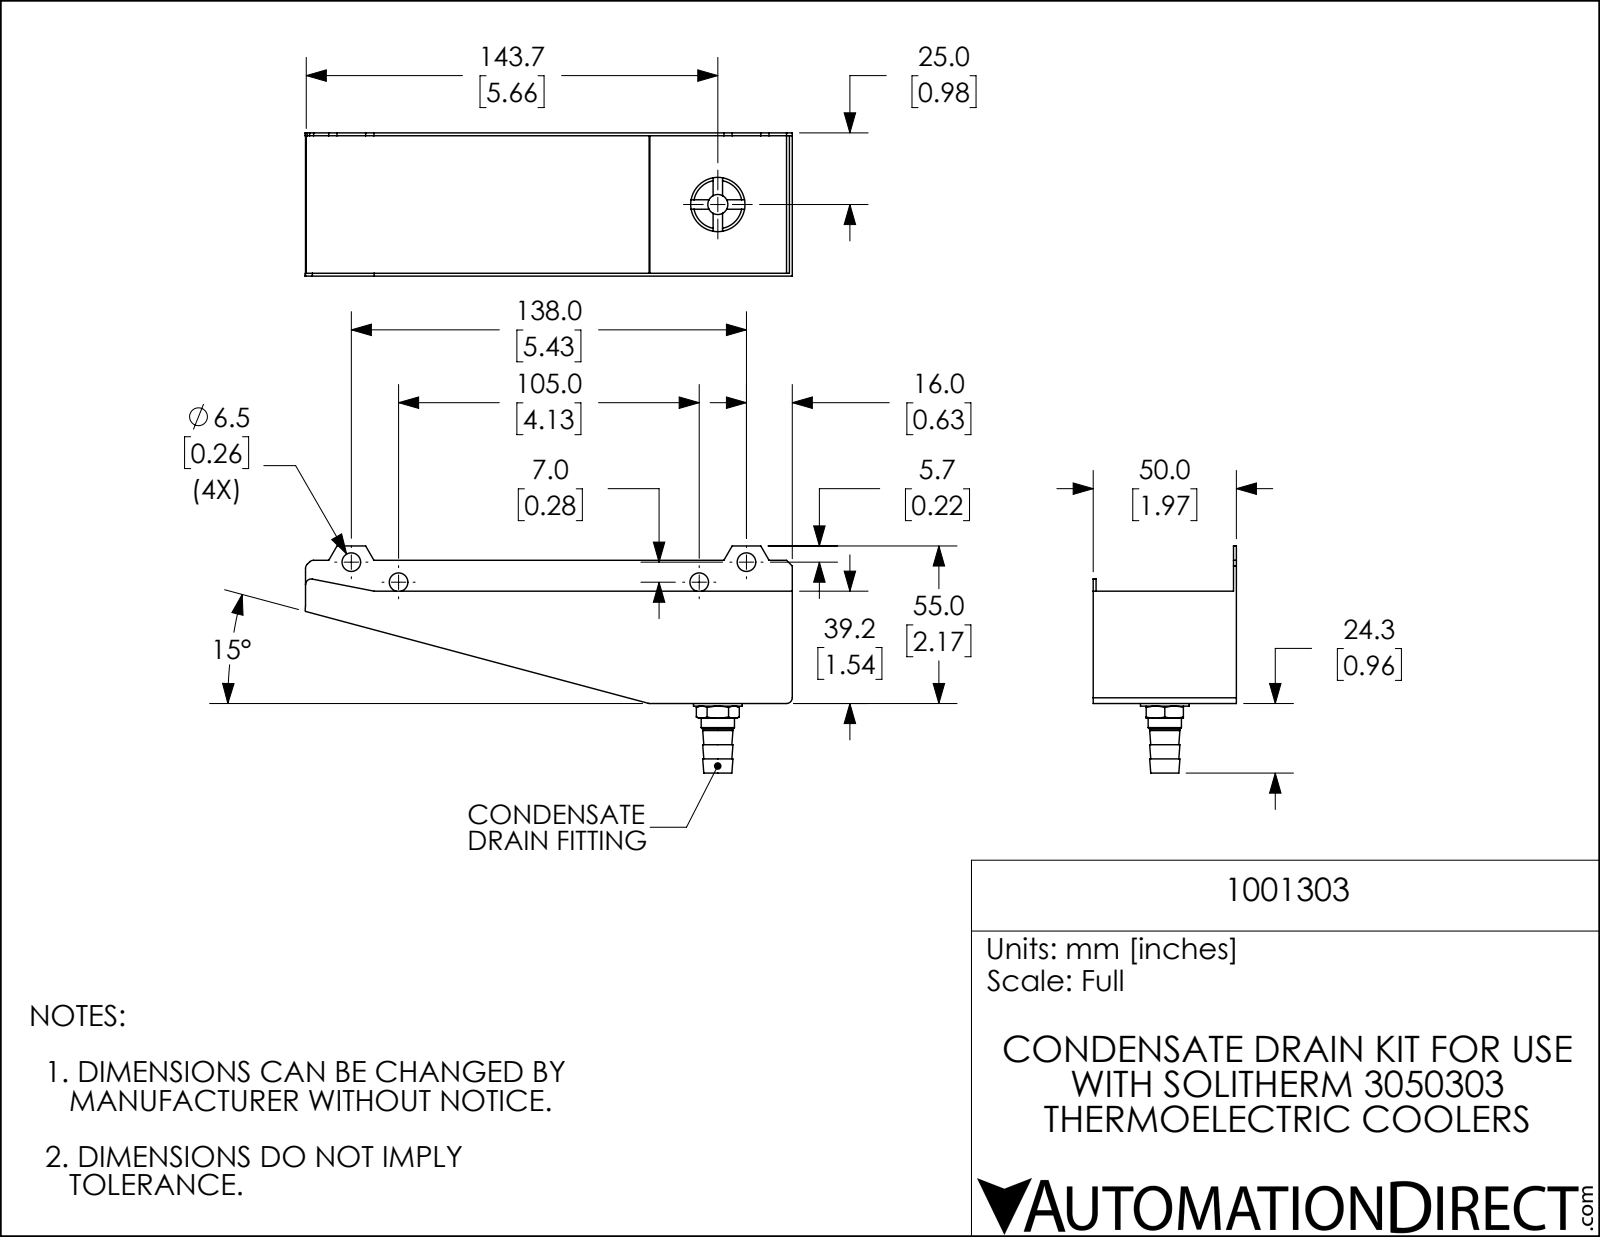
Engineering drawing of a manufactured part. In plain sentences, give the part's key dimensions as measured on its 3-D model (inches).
The part is named "1001303". Its 3-D file was written by "SolidWorks 2019 (AUTOMOTIVE_DESIGN)". It is 4 solids with 102 faces: 58 planar, 17 cylindrical and 27 other. Overall it measures 6.697 by 3.121 by 1.969 inches. Its volume is 1.434 cubic inches and its surface area 71.66 square inches. Round holes: 4 of diameter 0.256, 1 of diameter 0.276, 1 of diameter 0.433, 1 of diameter 0.484, 1 of diameter 0.515. Round bosses or shafts: 1 of diameter 0.746, 1 of diameter 0.669, 1 of diameter 0.457, 1 of diameter 0.387. Partial cylindrical surfaces (rounded edges, fillets, slot ends): 4 of radius 0.079, 1 of radius 0.039. The main face-to-face distances are 0.039, 1.929, 1.969, 1.89, 1.544, 1.505, 0.036, 0.075, 1.58, 2.004. The hole center spacings are 0.706, 4.791, 4.134, 5.433.
